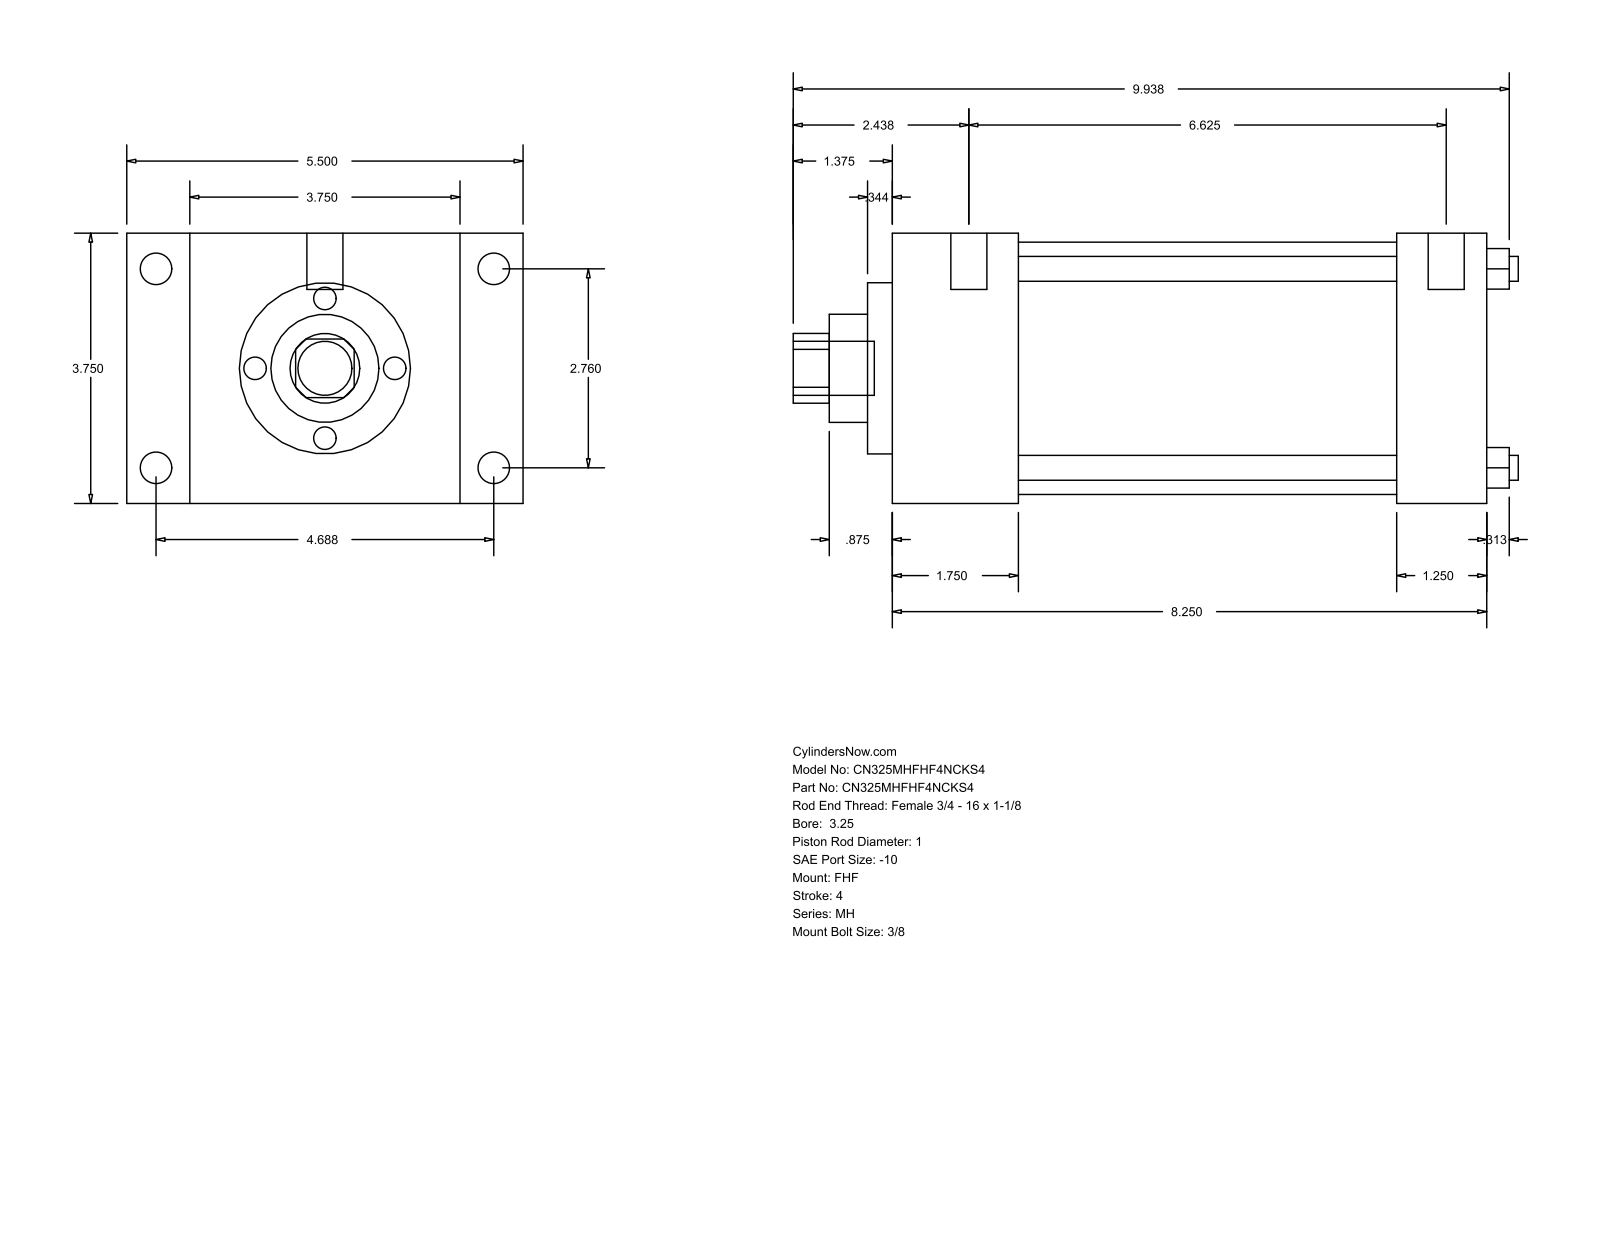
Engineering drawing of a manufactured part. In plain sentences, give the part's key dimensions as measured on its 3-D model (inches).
The part is named "MH_FHF__0325_1". Its 3-D file was written by "GSSL Pune (CONFIG_CONTROL_DESIGN)". It is 0 solids with 90 faces: 61 planar, 29 cylindrical and 0 other. Overall it measures 10.063 by 5.5 by 3.75 inches. Round holes: 4 of diameter 0.345, 1 of diameter 1, 1 of diameter 1.5, 1 of diameter 2.375, 1 of diameter 3.5. Round bosses or shafts: 4 of diameter 0.438, 4 of diameter 0.219, 2 of diameter 0.5, 1 of diameter 0.75. Partial cylindrical surfaces (rounded edges, fillets, slot ends): 1 of radius 0.484. The main face-to-face distances are 3.75, 8.25, 1.75, 6.5, 0.875, 4.625, 5.5, 7, 5.25, 1.25. The hole center spacings are 1.952, 2.76, 3.903.
